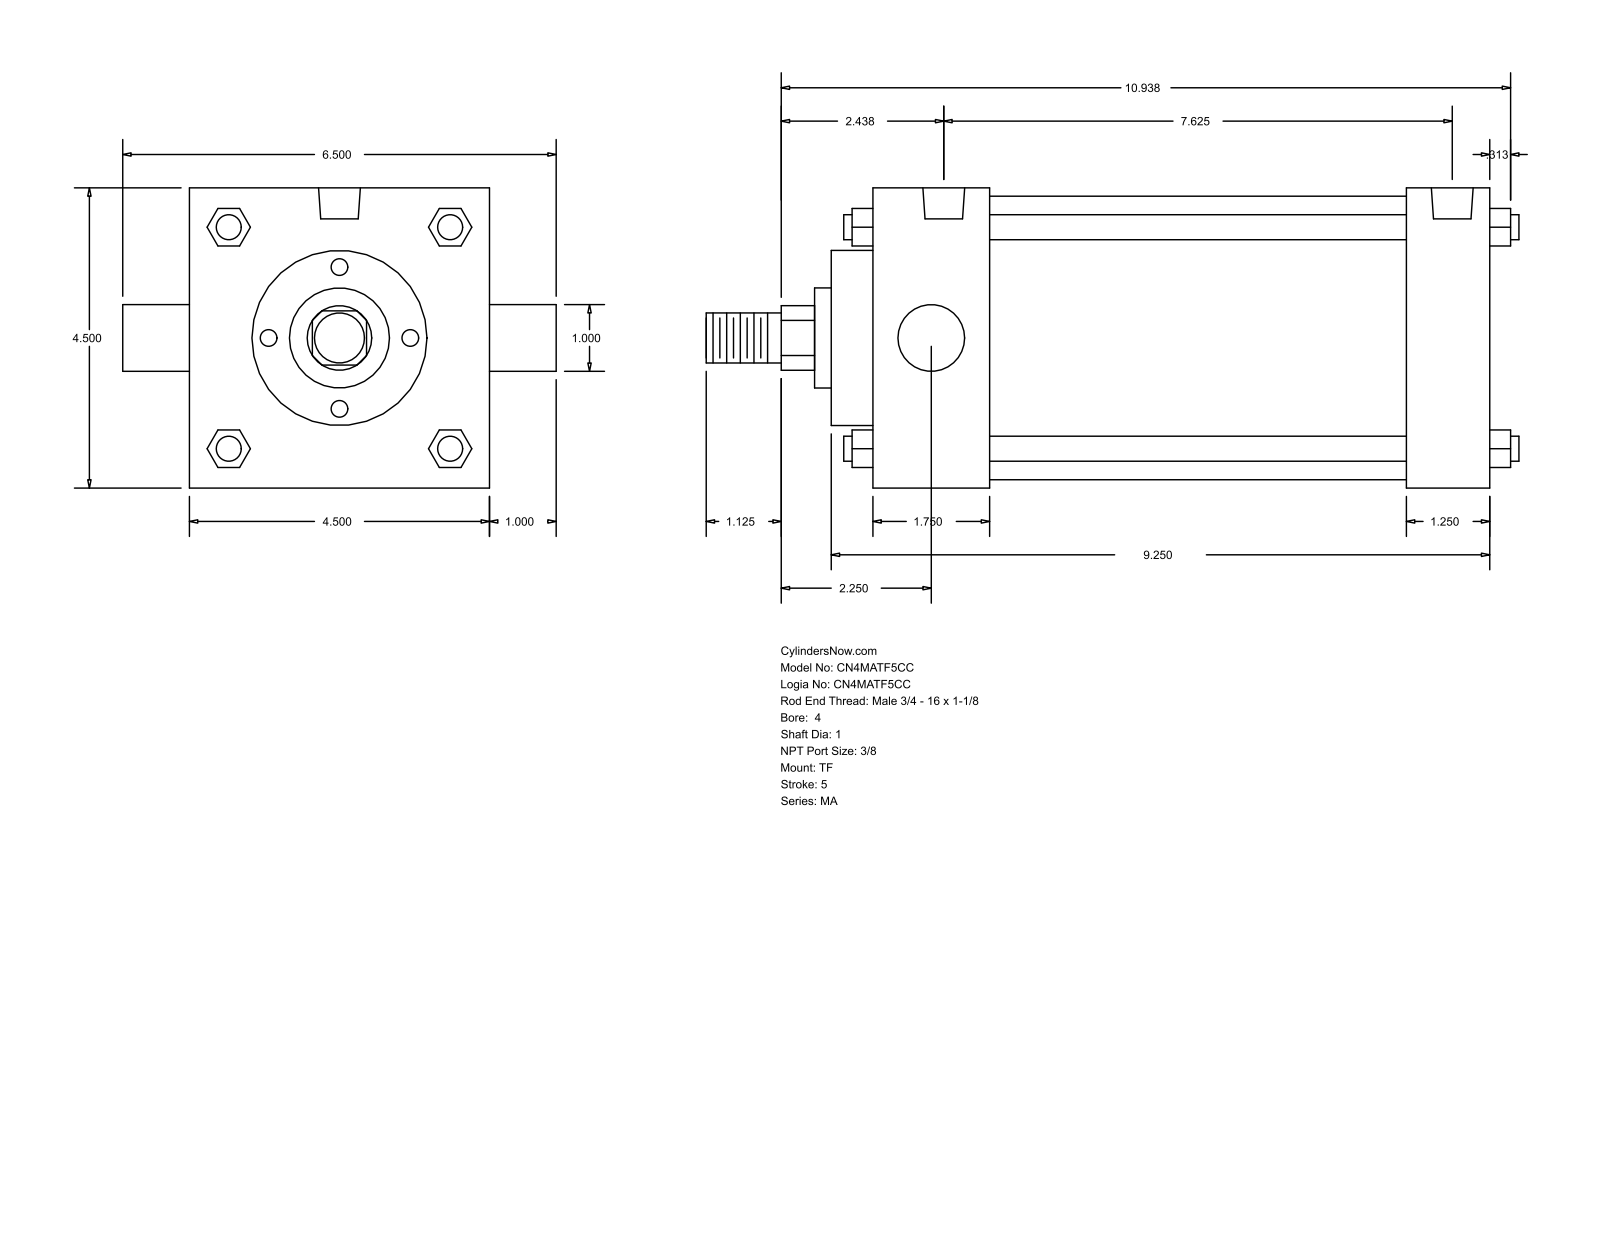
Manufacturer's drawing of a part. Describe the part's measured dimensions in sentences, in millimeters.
The part is named "MA_TF__0400_1". Its 3-D file was written by "GSSL Pune (CONFIG_CONTROL_DESIGN)". It is 0 solids with 122 faces: 93 planar, 29 cylindrical and 0 other. Overall it measures 309.56 by 165.1 by 114.3 millimeters. Round holes: 3 of diameter 11.11, 2 of diameter 15.93. Round bosses or shafts: 4 of diameter 9.53, 2 of diameter 25.4, 1 of diameter 107.95, 1 of diameter 66.67, 1 of diameter 38.1, 1 of diameter 19.05. Partial cylindrical surfaces (rounded edges, fillets, slot ends): 1 of radius 12.29. The main face-to-face distances are 114.3, 234.96, 203.2, 31.76, 44.46, 158.74, 190.5, 15.87, 60.33, 219.07. The hole center spacings are 4.76, 4.77, 184.15, 188.91, 188.92, 193.68.
